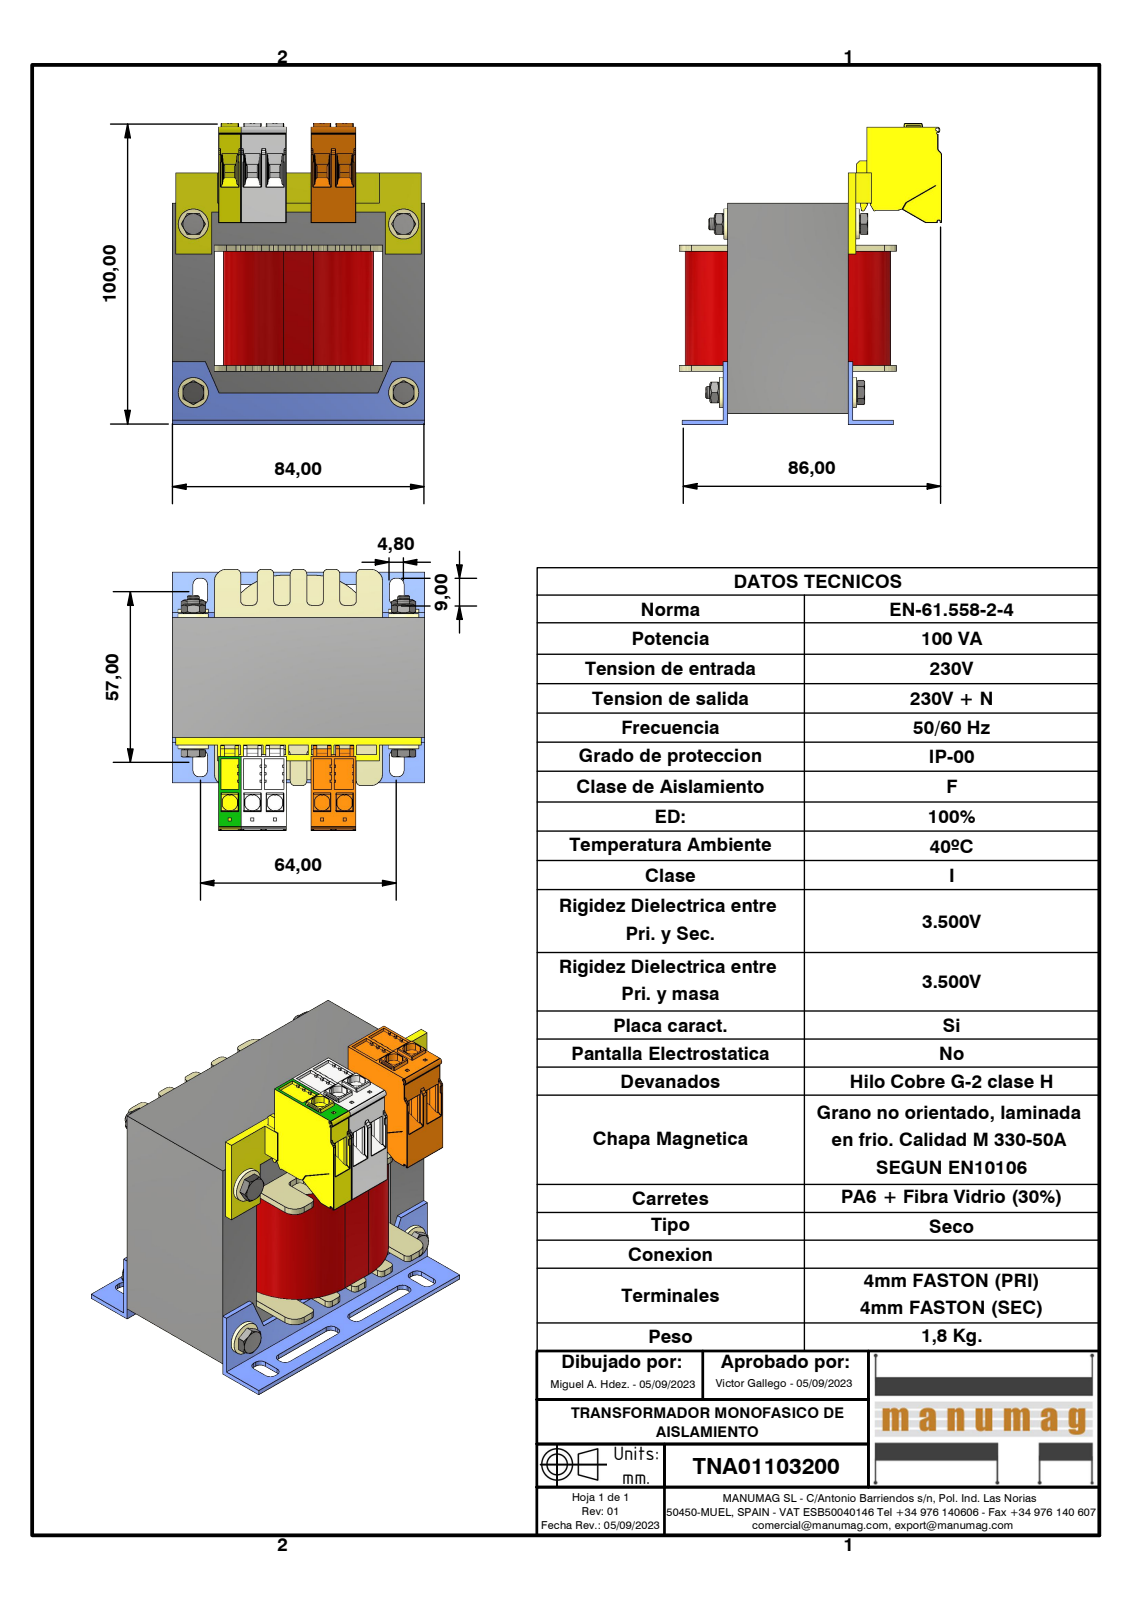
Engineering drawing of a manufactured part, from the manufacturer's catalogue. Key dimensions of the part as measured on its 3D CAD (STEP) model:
Part name (STEP PRODUCT): TNA01103200; EI84 x 70 - 40 (RC28); EI84; AF28DIN (+7 more)
STEP written by: Autodesk Inventor 2023 (AUTOMOTIVE_DESIGN)
Units: millimetres
Bodies: 24 solids, 5214 faces (4274 planar, 636 cylindrical, 304 other)
Overall size (bounding box): 100.2 × 86.95 × 84
Volume: 303 869 mm³ · Surface area: 91 423 mm²
Round holes (diameter × count): ⌀3.24 ×4, ⌀4 ×4, ⌀4.5 ×4
Round bosses / shafts (diameter × count): ⌀10 ×4, ⌀5.9 ×4, ⌀4.9 ×4, ⌀3.62 ×4
Partial cylindrical surfaces — rounded edges, fillets, slot ends (radius × count): R0.15 ×214, R0.2 ×58, R2 ×40, R1.5 ×32, R0.5 ×14, R0.3 ×6, R5 ×6, R2.7 ×5
Main face-to-face distances: 14, 56, 40, 28, 42, 70, 1.5, 2, 54, 84
Hole centre spacings: 56, 70, 89.64
